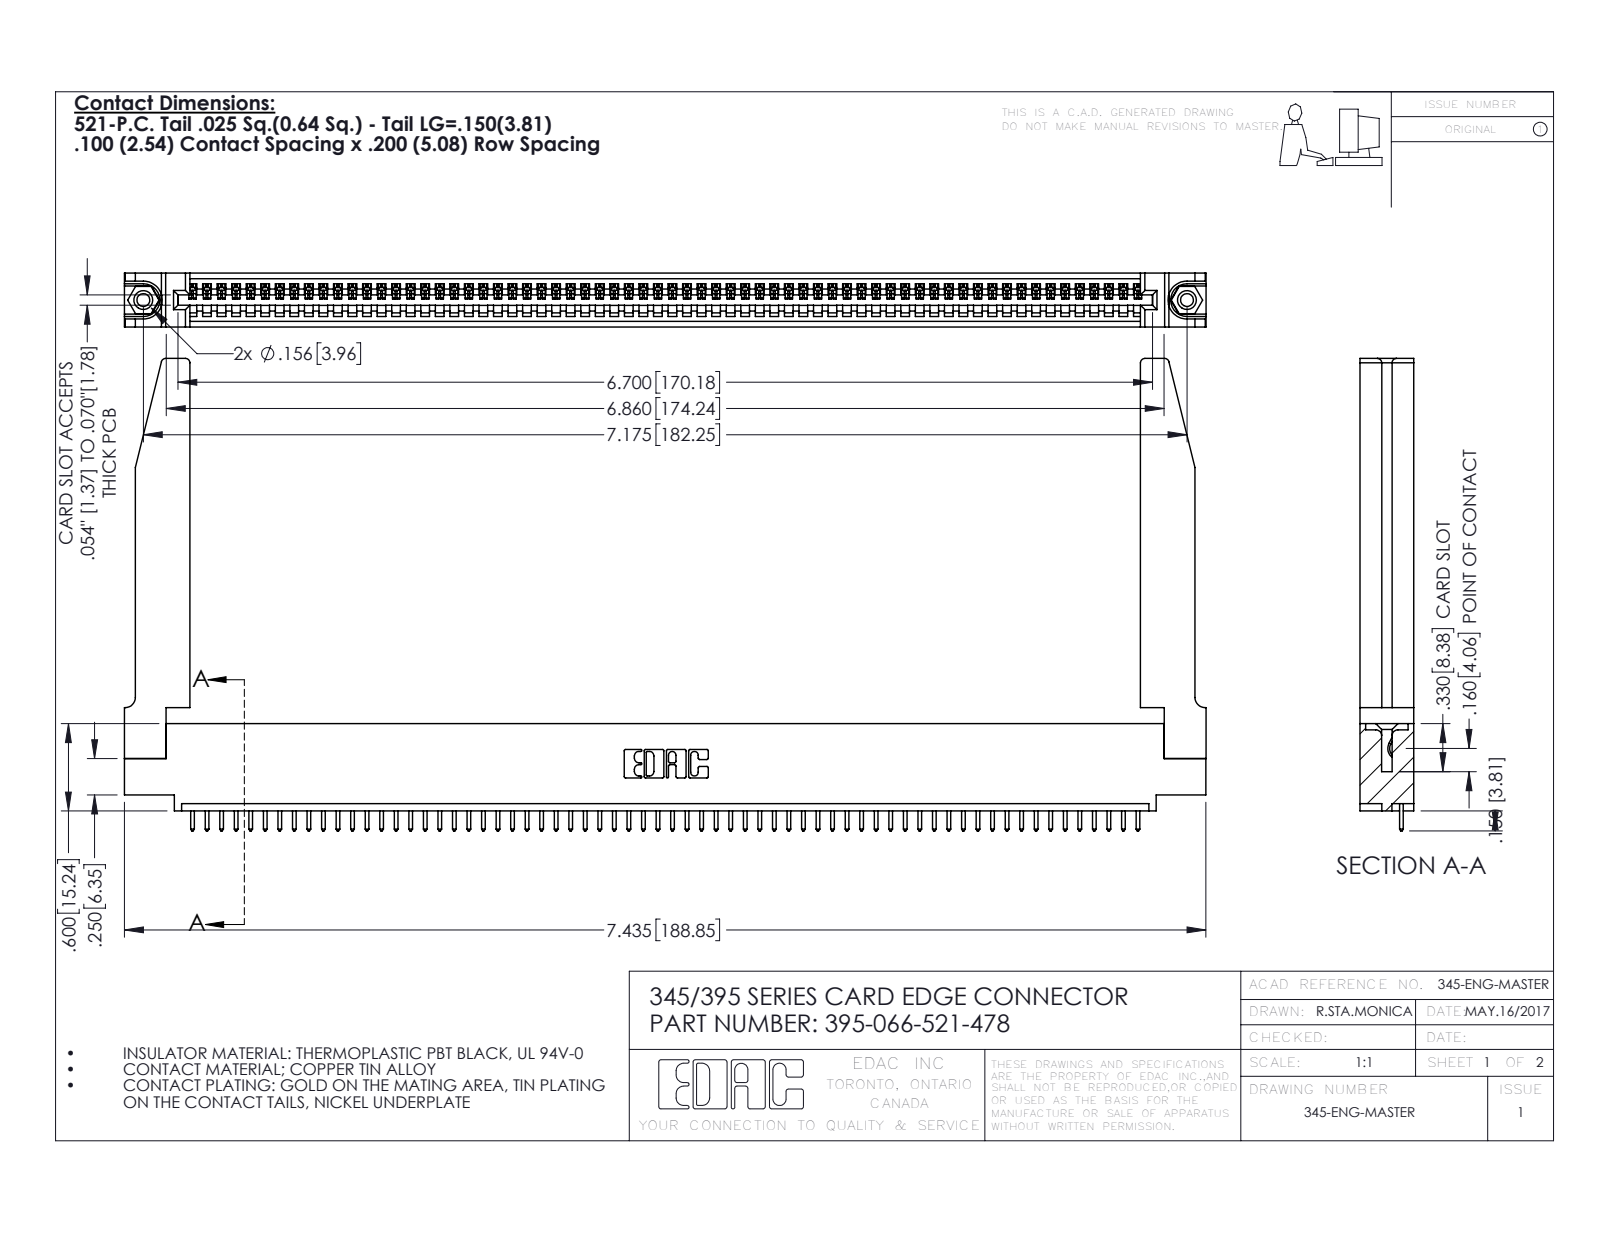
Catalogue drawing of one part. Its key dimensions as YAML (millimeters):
part_name: "345 Part_0.110 Offset - 0.156 Dia-TH; 345-220-078_345-220-078; 345-250-001_345-250-001-102; 345-292-001_345-293-121 (+1 more)"
step_written_by: "SolidWorks 2016 (CONFIG_CONTROL_DESIGN)"
units: millimeters
bodies: {solids: 71, faces: 4192, planar: 2866, cylindrical: 1274, other: 52}
overall_size: [188.9, 82.5, 9.4]
volume: 25650
surface_area: 30270
round_holes:
  - {diameter: 2.3, count: 2}
  - {diameter: 3.2, count: 2}
  - {diameter: 4, count: 2}
  - {diameter: 1.6, count: 1}
round_bosses_or_shafts:
  - {diameter: 3.9, count: 2}
partial_cylinders:
  - {radius: 0.2, count: 132}
  - {radius: 0.3, count: 132}
  - {radius: 0.3, count: 22}
  - {radius: 0.8, count: 8}
  - {radius: 0.2, count: 6}
  - {radius: 0.8, count: 6}
  - {radius: 0.7, count: 3}
  - {radius: 0.8, count: 2}
face_to_face_distances: [1.8, 9.4, 7.6, 2.5, 6.9, 0.6, 5.1, 5.7, 3.8, 3.8]
hole_center_spacings: [6.9, 176.3, 182.2]
